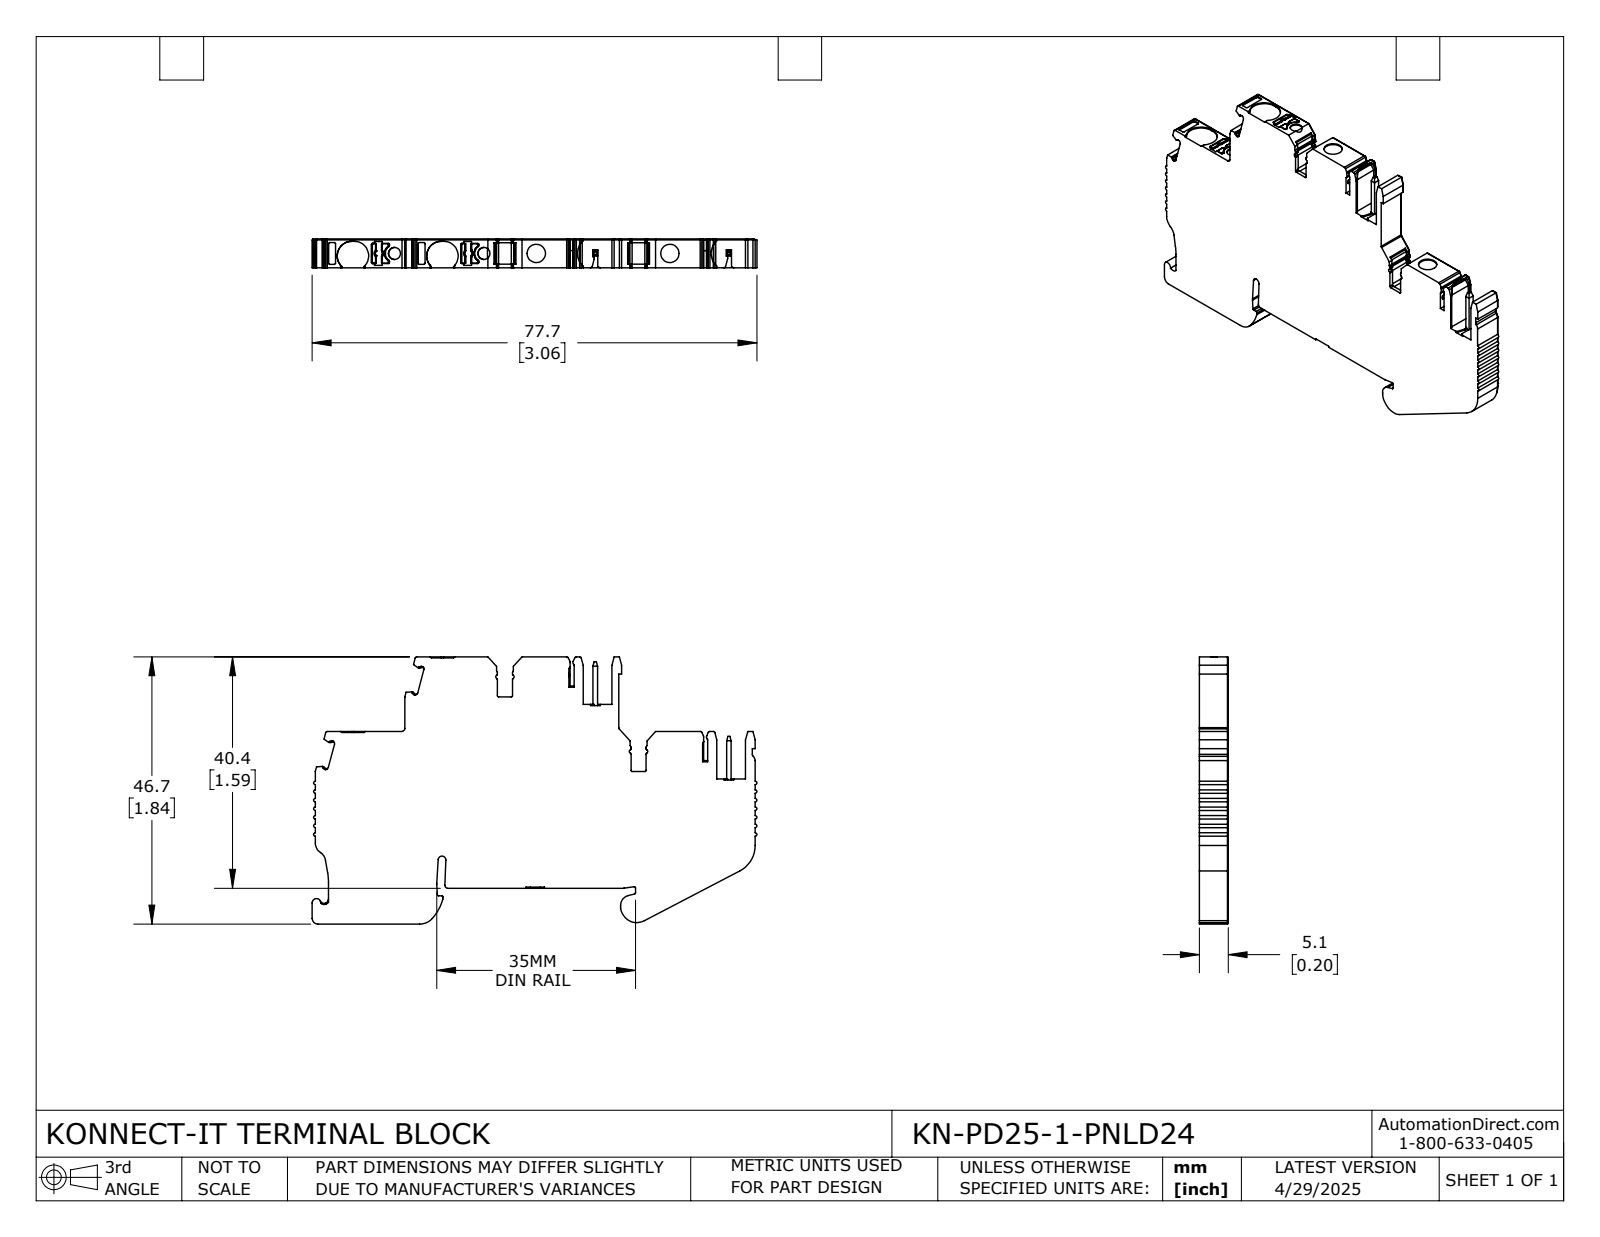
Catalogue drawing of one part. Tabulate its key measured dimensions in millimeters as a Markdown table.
| quantity | value |
| --- | --- |
| part name | KN-PD25-1-PNLD24 |
| STEP written by | SolidWorks 2024 (CONFIG_CONTROL_DESIGN) |
| units | millimeters |
| bodies | 1 solid, 731 faces (387 planar, 304 cylindrical, 40 other) |
| overall size | 77.6 × 46.7 × 5.1 |
| volume | 12 900 mm³ |
| surface area | 7 019 mm² |
| round holes (diameter × count) | 2.1 × 2, 3.2 × 2 |
| partial cylindrical surfaces (radius × count) | 0.2 × 58, 0.3 × 48, 0.1 × 23, 0.4 × 16, 0.5 × 16, 0.2 × 8, 0.6 × 6, 0.2 × 4 |
| main face-to-face distances | 5.1, 13, 23.3, 6.2, 33.6, 27.4, 46.7, 40.4, 5.2, 27.2 |
| hole center spacings | 9.1, 15.6, 23.3, 24.8, 32.5, 48.1 |
